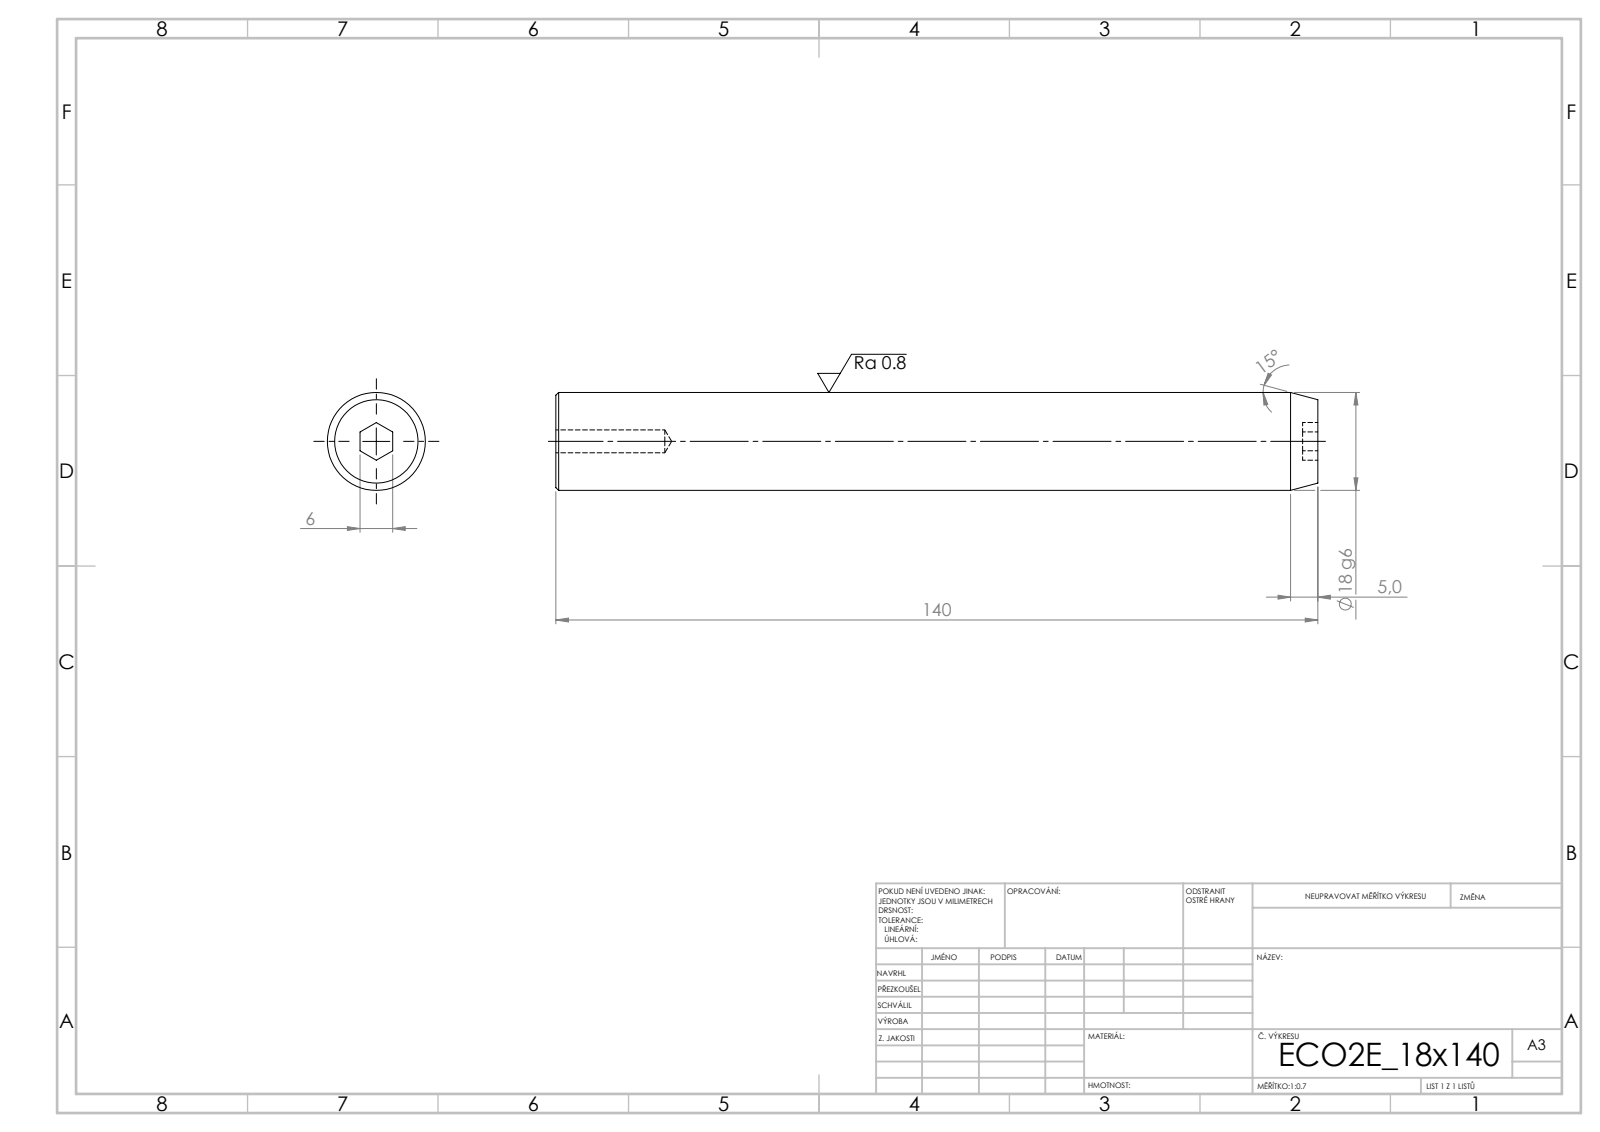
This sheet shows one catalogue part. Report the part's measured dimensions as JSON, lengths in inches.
{"step_written_by": "SolidWorks 2019 (CONFIG_CONTROL_DESIGN)", "units": "inches", "bodies": {"solids": 1, "faces": 19, "planar": 9, "cylindrical": 4, "other": 6}, "overall_size": [5.512, 0.709, 0.709], "volume_in3": 2.14, "surface_area_in2": 13.41, "round_holes": [[0.165, 1]], "round_bosses_or_shafts": [[0.709, 1]], "face_to_face_distances": [5.512, 0.11, 5.402, 0.236]}
